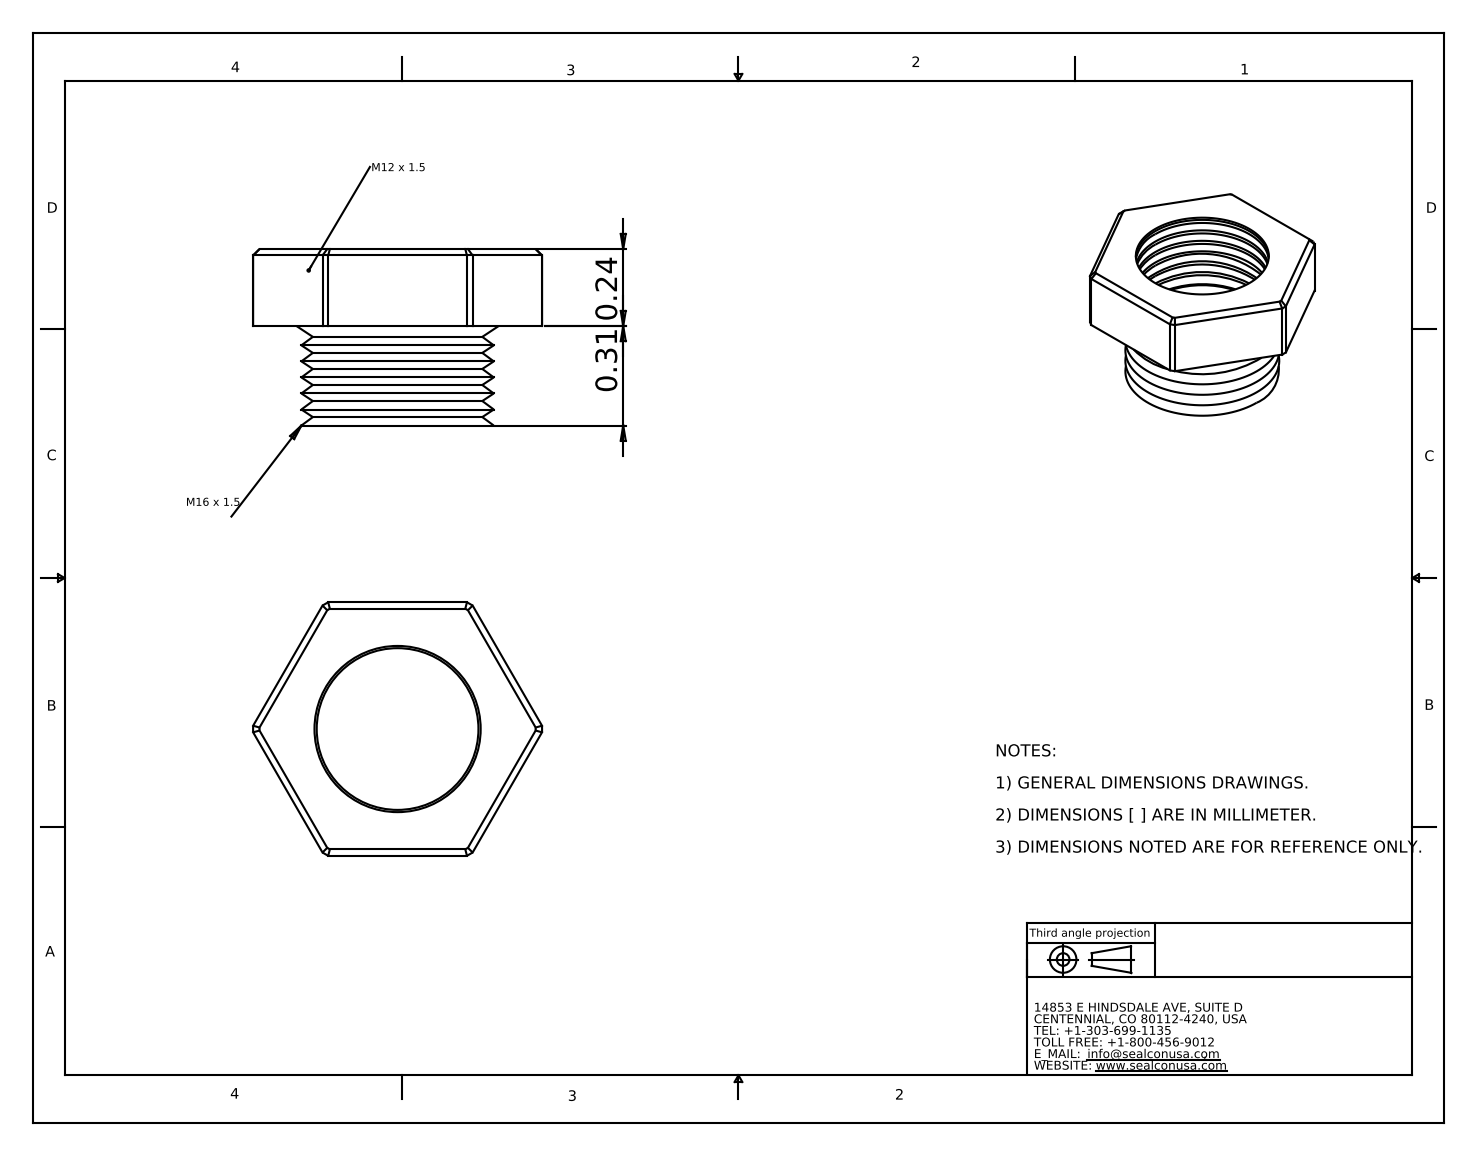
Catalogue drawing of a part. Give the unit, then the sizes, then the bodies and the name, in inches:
Units: inches
Overall size (bounding box): 0.901 × 0.79 × 0.41
Round holes (diameter × count): ⌀0.504 ×1, ⌀0.518 ×1
Partial cylindrical surfaces — rounded edges, fillets, slot ends (radius × count): R0.45 ×1
Main face-to-face distances: 0.17, 0.79, 0.24, 0.41, 0.093, 0.147, 0.317
Volume: 0.065 in³ · Surface area: 2.561 in²
Bodies: 1 solid, 90 faces (16 planar, 23 cylindrical, 51 other)
Part name (STEP PRODUCT): RM-1612-BK
STEP written by: SolidWorks 2008 (CONFIG_CONTROL_DESIGN)
